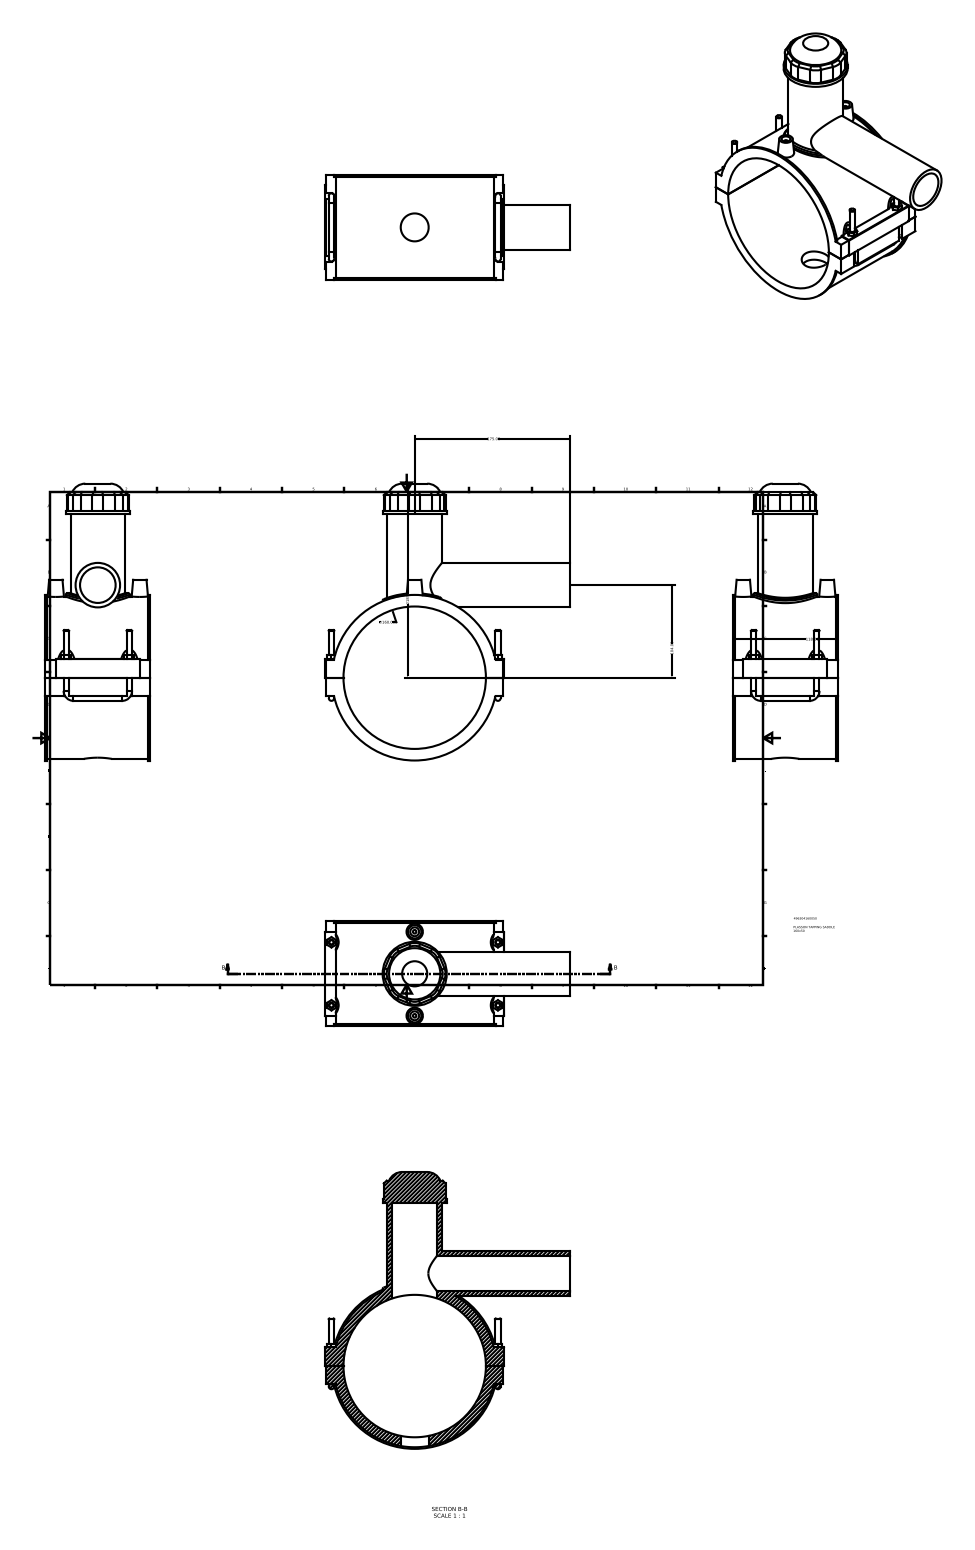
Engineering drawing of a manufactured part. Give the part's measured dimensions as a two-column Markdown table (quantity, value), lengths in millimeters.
| quantity | value |
| --- | --- |
| part name | 496304160050 |
| STEP written by | Autodesk Inventor 2015 (AUTOMOTIVE_DESIGN) |
| units | millimeters |
| bodies | 1 solid, 181 faces (110 planar, 47 cylindrical, 24 other) |
| overall size | 311.02 × 275.5 × 118 |
| volume | 1 087 000 mm³ |
| surface area | 250 540 mm² |
| round holes (diameter × count) | 10 × 2, 31.36 × 1, 40 × 1, 50.4 × 1, 160 × 1 |
| round bosses / shafts (diameter × count) | 6 × 6, 4 × 2, 186.05 × 1, 182.4 × 1, 72 × 1, 61.2 × 1, 50 × 1 |
| partial cylindrical surfaces (radius × count) | 16 × 8, 3 × 4, 7.5 × 4, 0.5 × 1, 94.85 × 1 |
| main face-to-face distances | 118, 1, 200, 183.55, 183.45, 199, 19.95, 20.05, 203.5, 201 |
| hole center spacings | 47.2, 94.4 |
